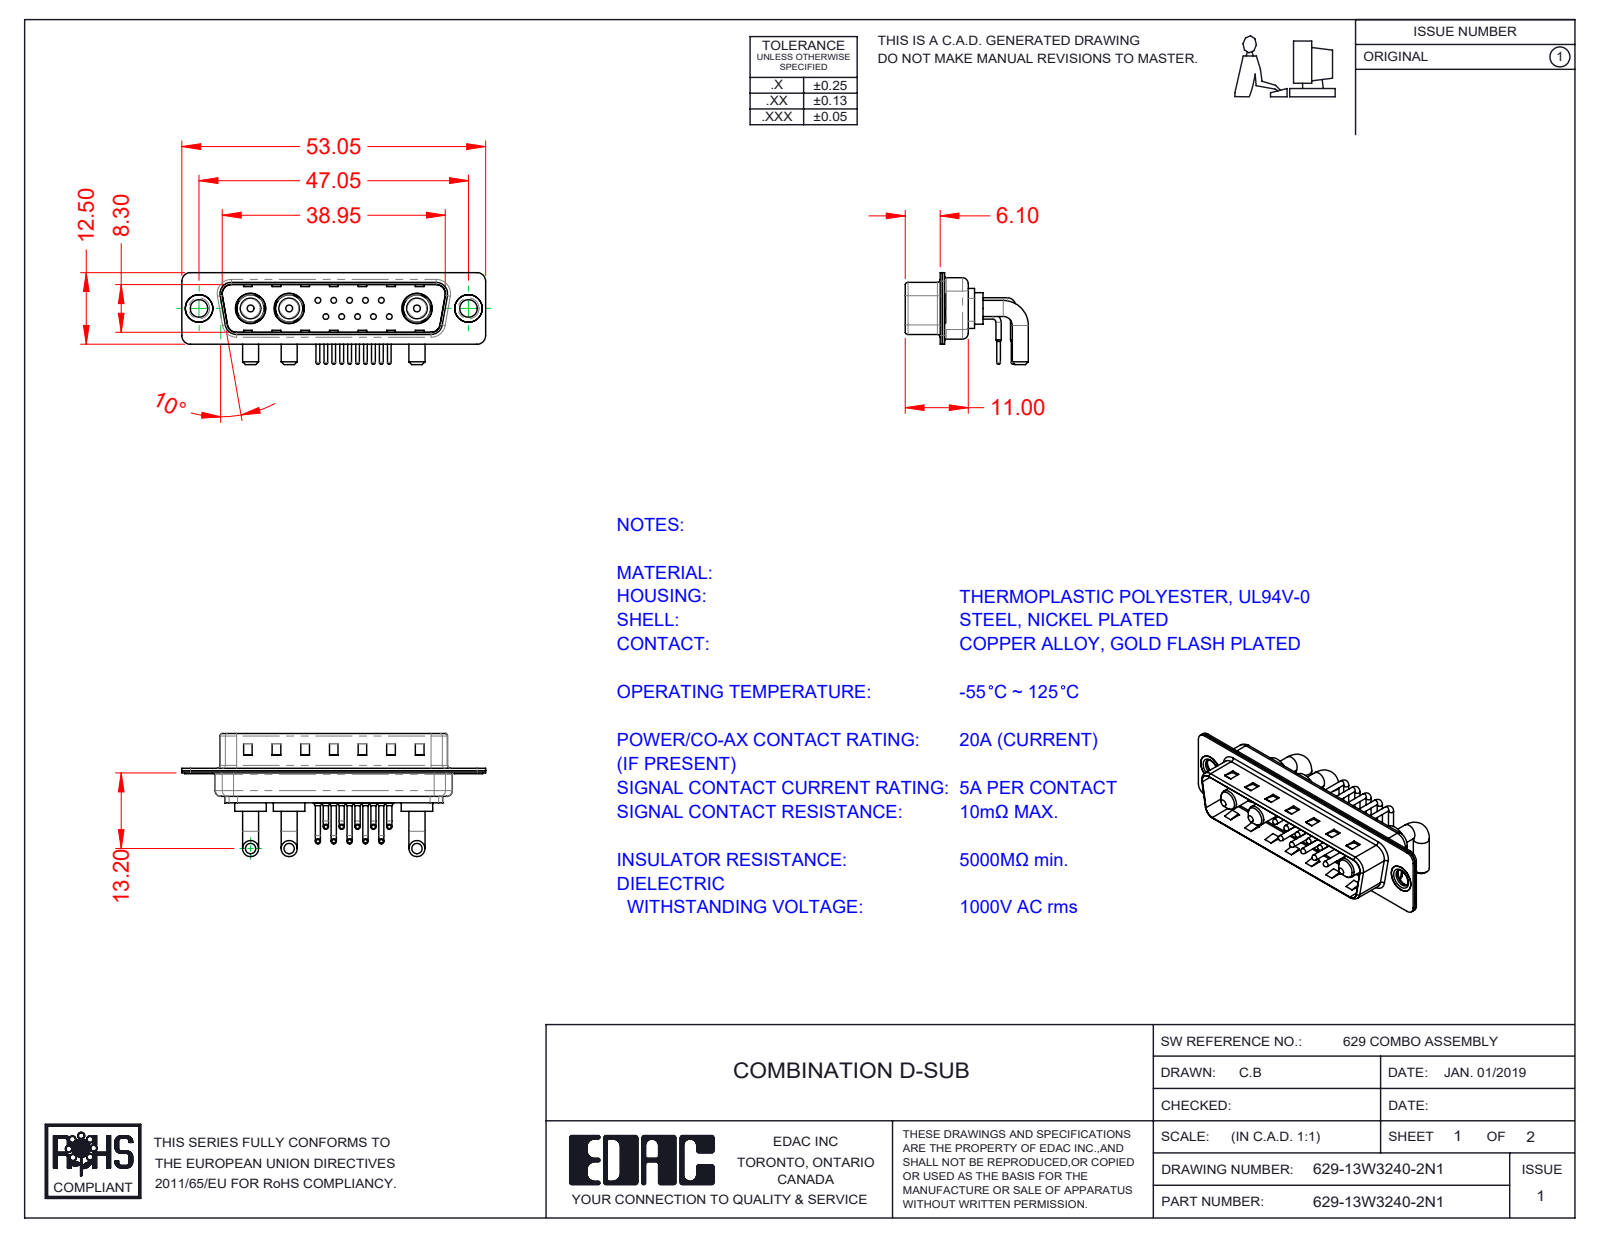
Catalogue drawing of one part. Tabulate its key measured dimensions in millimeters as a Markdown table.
| quantity | value |
| --- | --- |
| part name | 629Combo Shell Front_25 Contacts; 629-13W3240-2N1; 629Combo Contact Row 1; 629Combo Thru Hole Rivet (+4 more) |
| STEP written by | SolidWorks 2020 (CONFIG_CONTROL_DESIGN) |
| units | millimeters |
| bodies | 21 solids, 1579 faces (841 planar, 544 cylindrical, 194 other) |
| overall size | 53.05 × 21.5 × 16.05 |
| volume | 3 132 mm³ |
| surface area | 7 226 mm² |
| round holes (diameter × count) | 0.75 × 10, 1.6 × 10, 2 × 10, 4.85 × 3, 5.3 × 3, 3.05 × 2, 4 × 2, 4.8 × 2 |
| round bosses / shafts (diameter × count) | 0.9 × 20, 1.5 × 10, 1 × 10, 0.65 × 10, 2.8 × 6, 5.5 × 3, 5.2 × 3, 4.75 × 3 |
| partial cylindrical surfaces (radius × count) | 1.5 × 16, 2 × 12, 1.01 × 10, 0.5 × 8, 1.6 × 8, 0.25 × 4, 0.6 × 4, 0.65 × 4 |
| main face-to-face distances | 0.4, 0.8, 9.5, 9.1, 8.7, 9.9, 5.6, 0.75, 1.2, 0.35 |
| hole center spacings | 3.16, 2.77, 5.04, 5.54, 7.49, 5.03, 8.31, 10.11 |
